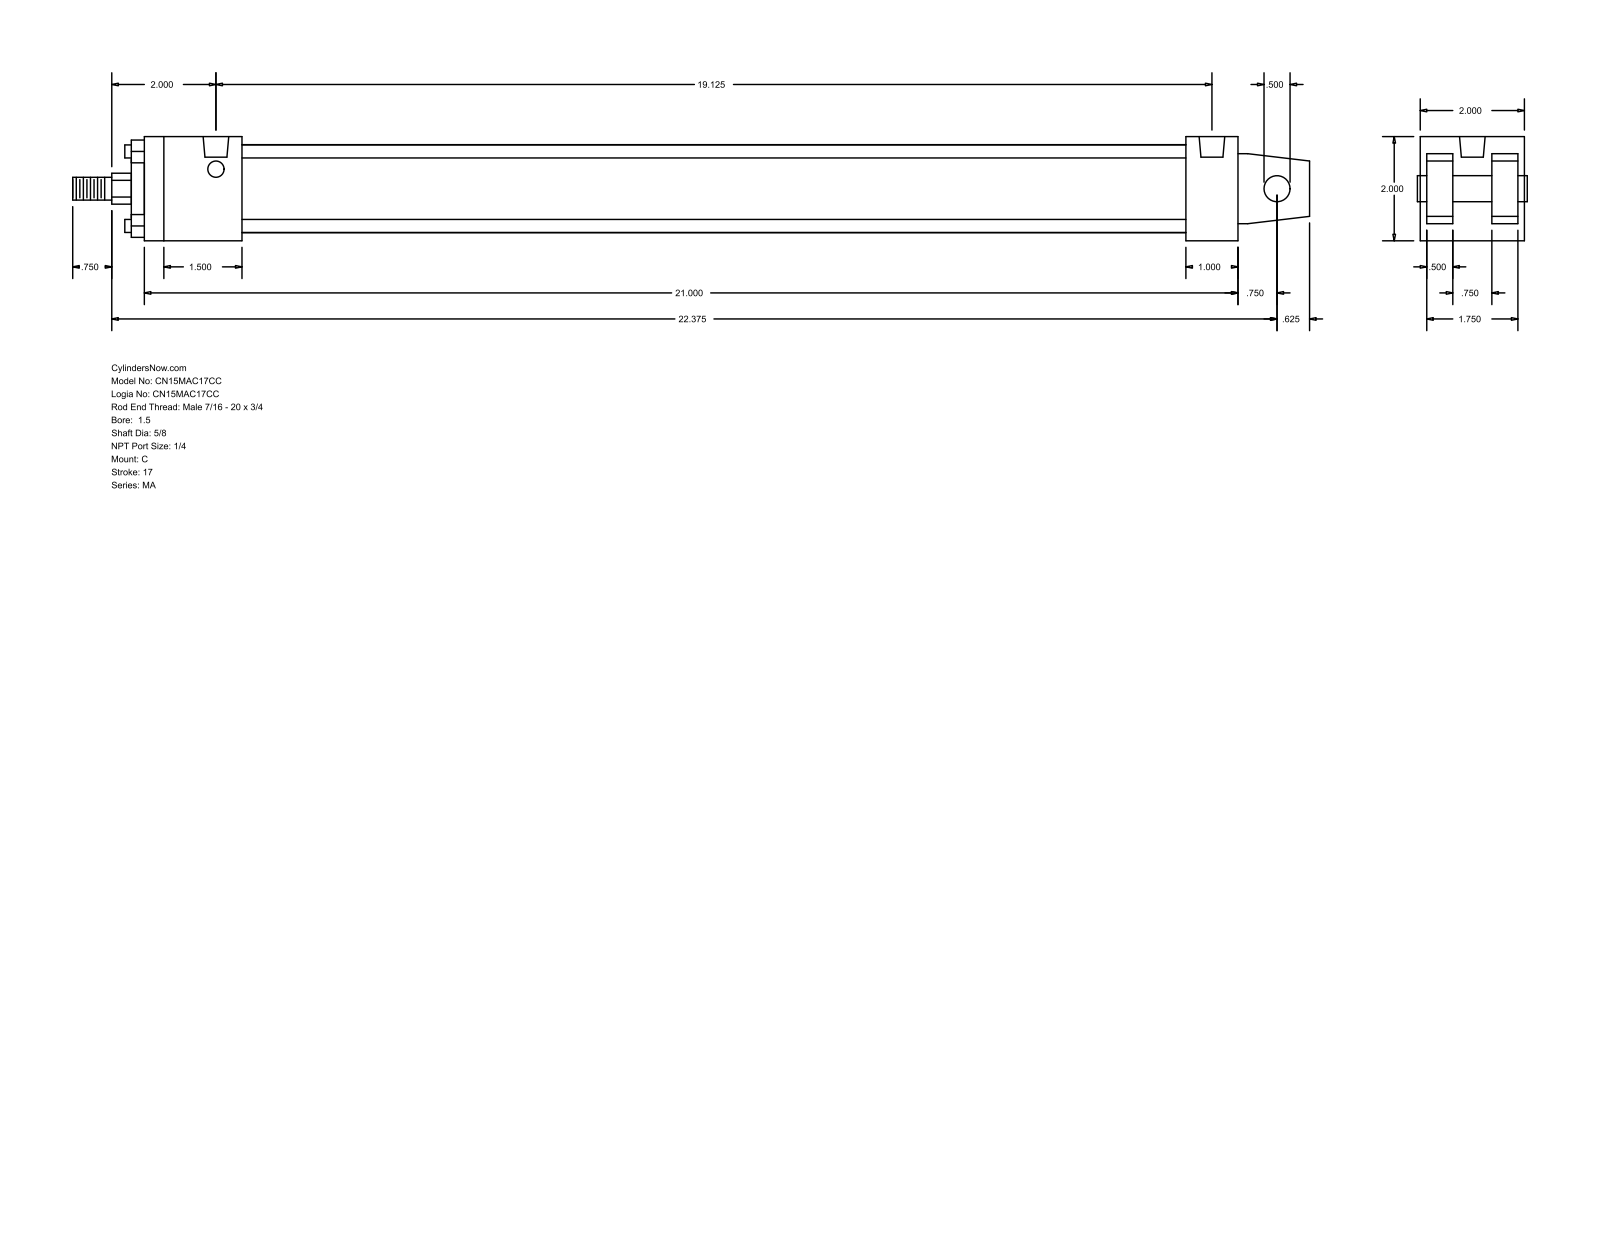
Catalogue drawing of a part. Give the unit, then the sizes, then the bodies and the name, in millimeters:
Units: millimetres
Overall size (bounding box): 603.25 × 50.8 × 50.8
Round holes (diameter × count): ⌀7.94 ×4, ⌀12.49 ×2
Round bosses / shafts (diameter × count): ⌀6.35 ×4, ⌀42.93 ×1, ⌀28.57 ×1, ⌀15.88 ×1, ⌀12.7 ×1, ⌀11.11 ×1
Partial cylindrical surfaces — rounded edges, fillets, slot ends (radius × count): R7.54 ×1
Main face-to-face distances: 50.8, 34.93, 12.7, 15.87, 3.17, 47.63, 31.76, 533.39, 508, 25.39
Hole centre spacings: 485.78
Bodies: 0 solids, 103 faces (76 planar, 27 cylindrical, 0 other)
Part name (STEP PRODUCT): MA_C__0150_0.625
STEP written by: GSSL Pune (CONFIG_CONTROL_DESIGN)
